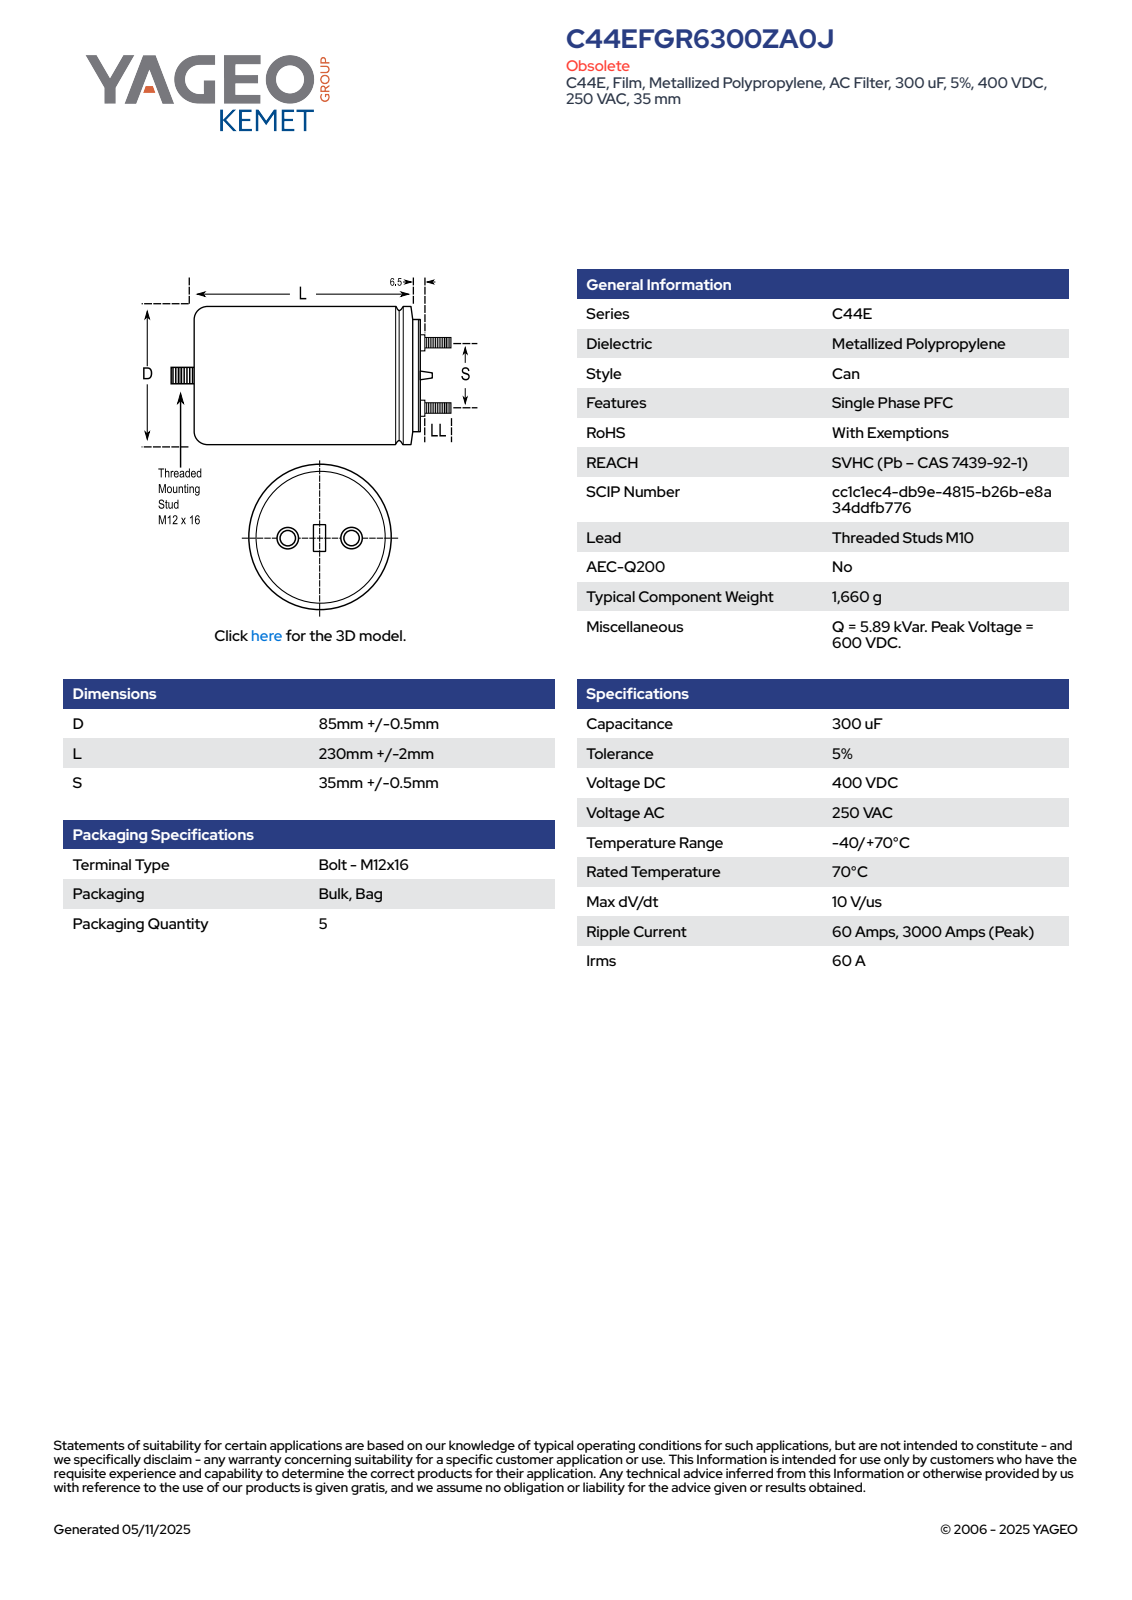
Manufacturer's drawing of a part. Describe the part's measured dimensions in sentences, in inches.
The part is named "CFP_C44E_85X230_D85.5L232S35.5LL25". Its 3-D file was written by "SolidWorks 2014 (AUTOMOTIVE_DESIGN)". It is 1 solid with 103 faces: 34 planar, 34 cylindrical and 35 other. Overall it measures 11.004 by 3.367 by 3.366 inches. Its volume is 82.5 cubic inches and its surface area 121.6 square inches. Round bosses or shafts: 2 of diameter 0.591, 2 of diameter 0.394, 1 of diameter 3.366, 1 of diameter 2.677, 1 of diameter 0.472. Partial cylindrical surfaces (rounded edges, fillets, slot ends): 1 of radius 1.683. The main face-to-face distances are 9.291, 9.134, 0.157, 9.39, 0.256, 0.098, 9.567, 0.433, 0.276, 0.177.
